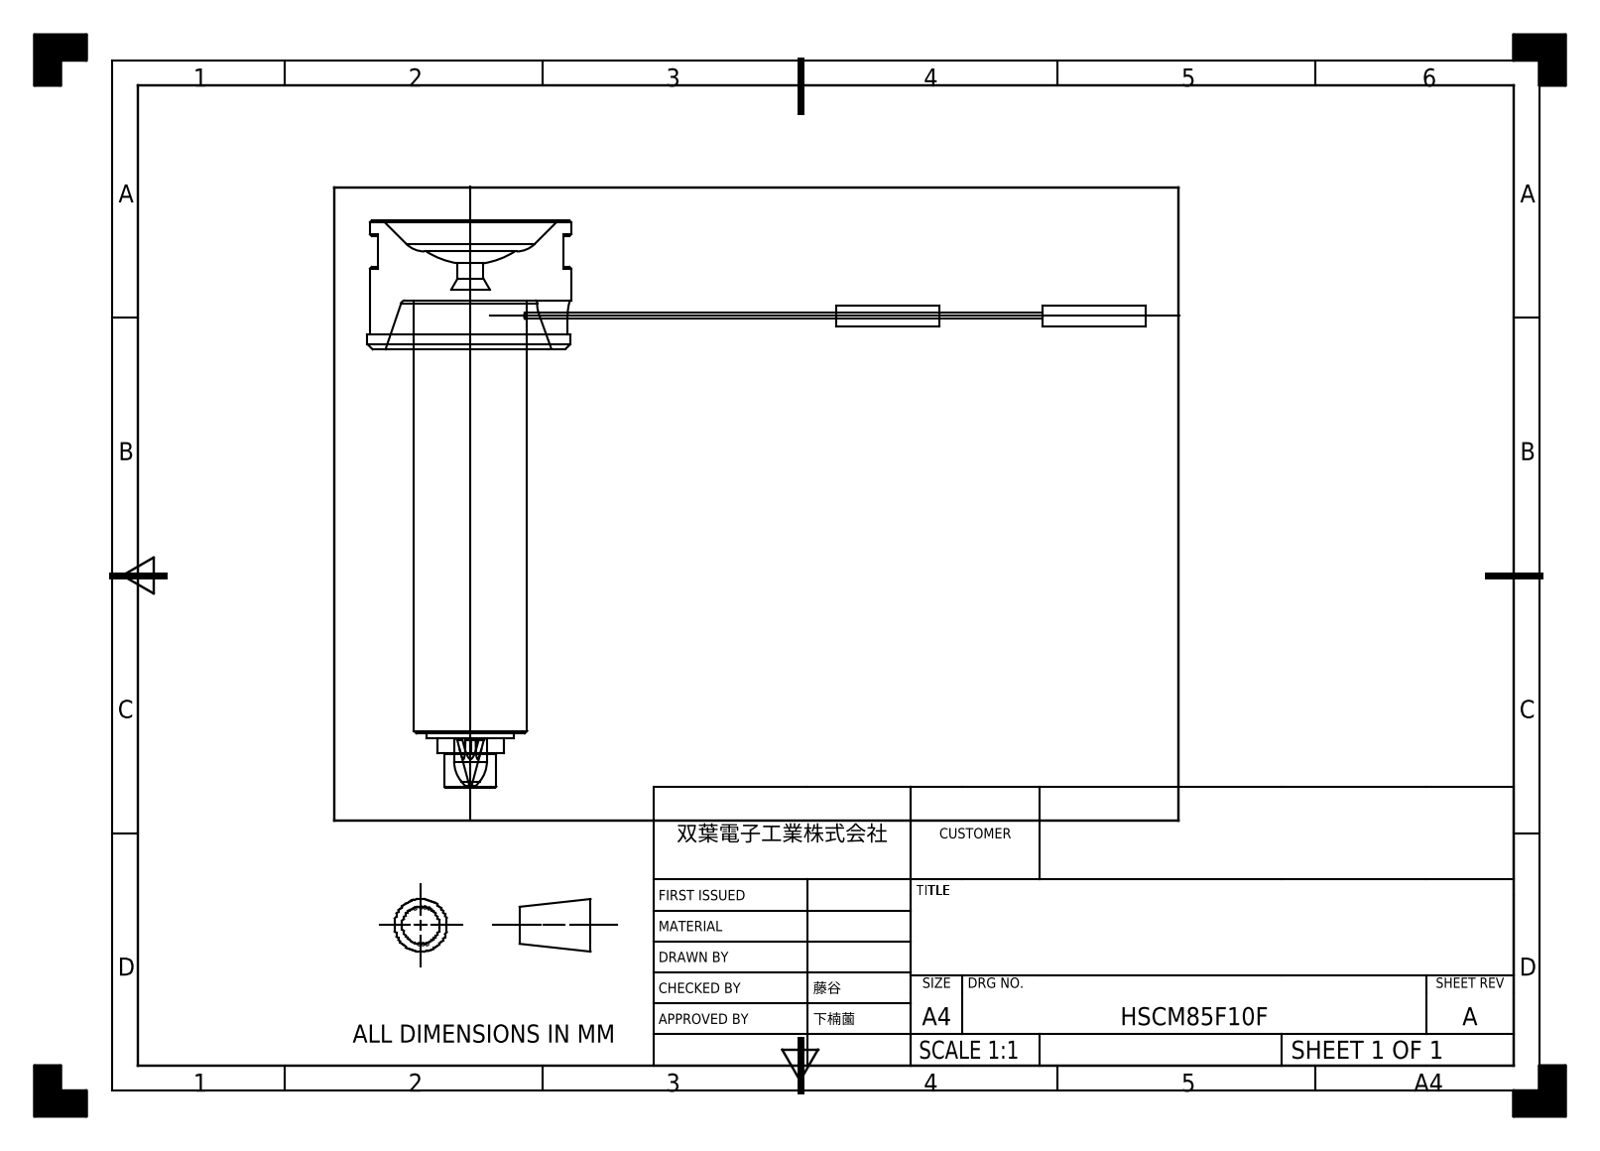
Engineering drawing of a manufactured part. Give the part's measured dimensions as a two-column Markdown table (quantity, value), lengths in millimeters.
| quantity | value |
| --- | --- |
| part name | HSCM85F10F |
| STEP written by | SIEMENS PLM Software NX 2023 (AUTOMOTIVE_DESIGN) |
| units | millimeters |
| bodies | 1 solid, 74 faces (30 planar, 23 cylindrical, 21 other) |
| overall size | 151 × 110 × 40 |
| volume | 52 189 mm³ |
| surface area | 14 009 mm² |
| round holes (diameter × count) | 2 × 1, 5 × 1, 6.35 × 1 |
| round bosses / shafts (diameter × count) | 4 × 2, 1.2 × 2, 40 × 1, 39 × 1, 22 × 1, 16.9 × 1, 10 × 1 |
| partial cylindrical surfaces (radius × count) | 2.8 × 3, 3 × 2, 7.45 × 1 |
| main face-to-face distances | 25, 9.5, 85, 15.5, 99.5, 84, 74.5, 3, 100.5, 75.5 |
